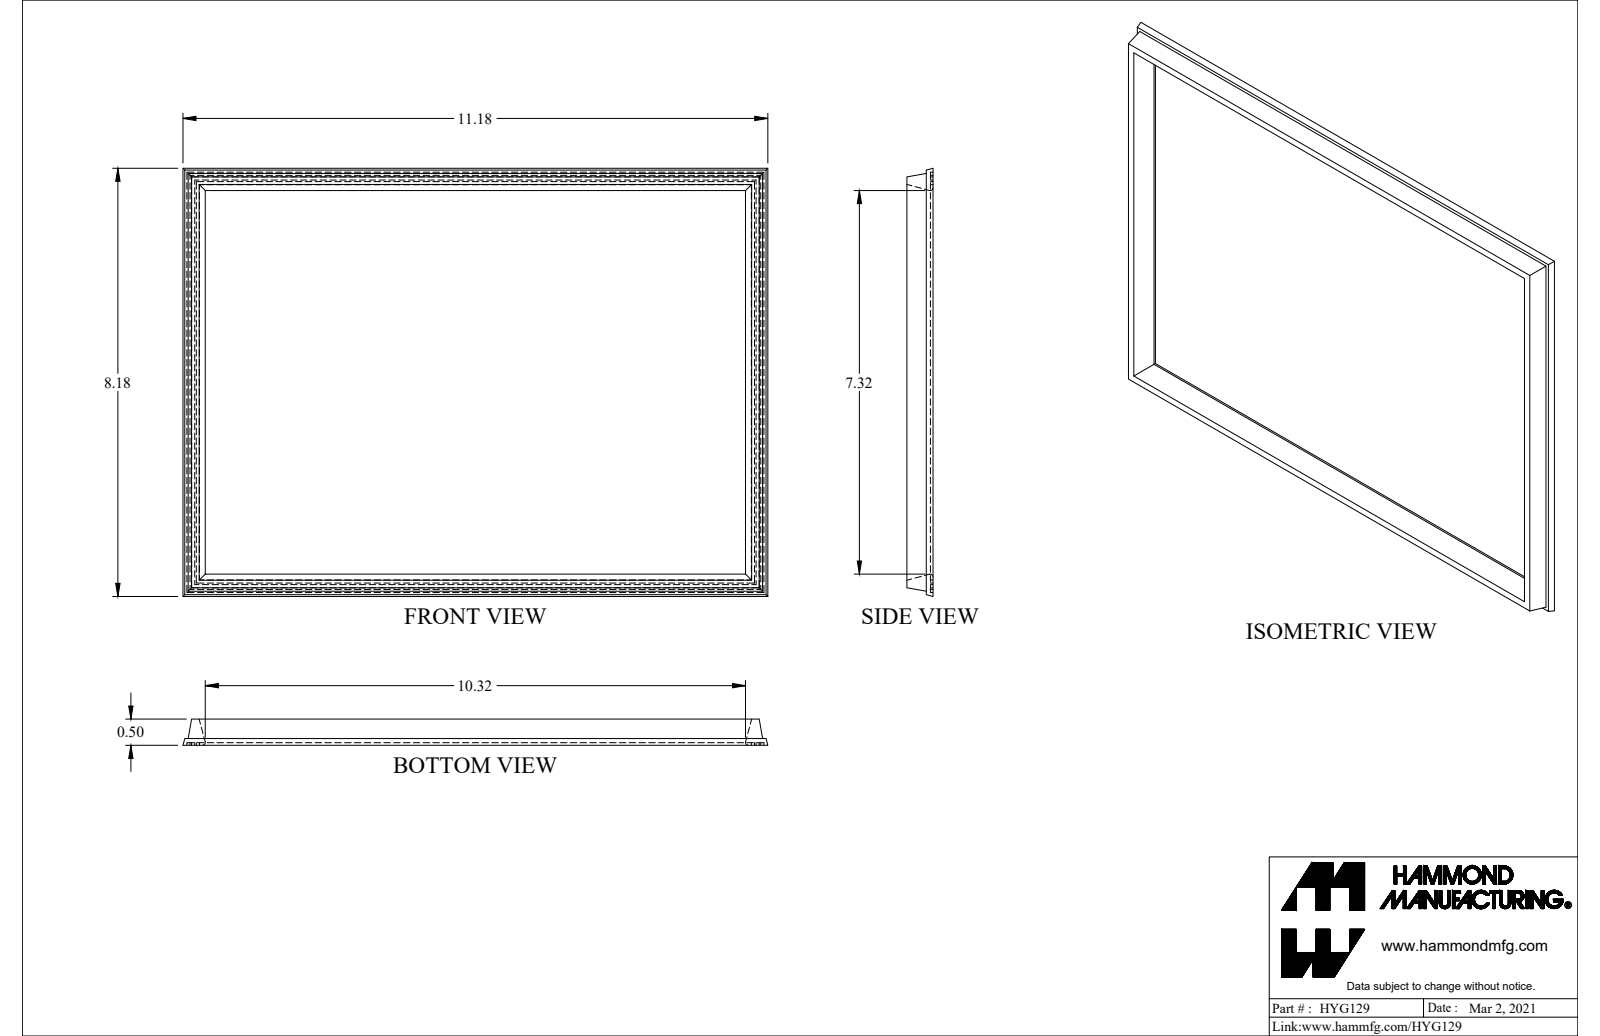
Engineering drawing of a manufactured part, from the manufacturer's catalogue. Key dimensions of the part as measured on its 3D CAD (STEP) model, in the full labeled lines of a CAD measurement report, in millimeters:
Part name (STEP PRODUCT): HYG129
STEP written by: SolidWorks 2021 (AUTOMOTIVE_DESIGN)
Units: millimetres
Bodies: 1 solid, 49 faces (45 planar, 4 cylindrical, 0 other)
Overall size (bounding box): 283.9 × 207.7 × 12.7
Volume: 76 310 mm³ · Surface area: 46 210 mm²
Partial cylindrical surfaces — rounded edges, fillets, slot ends (radius × count): R1.4 ×4
Main face-to-face distances: 1.3, 12.7, 11.4, 2.3, 1.5, 3.8, 197.8, 189.8, 0.8, 2.3
